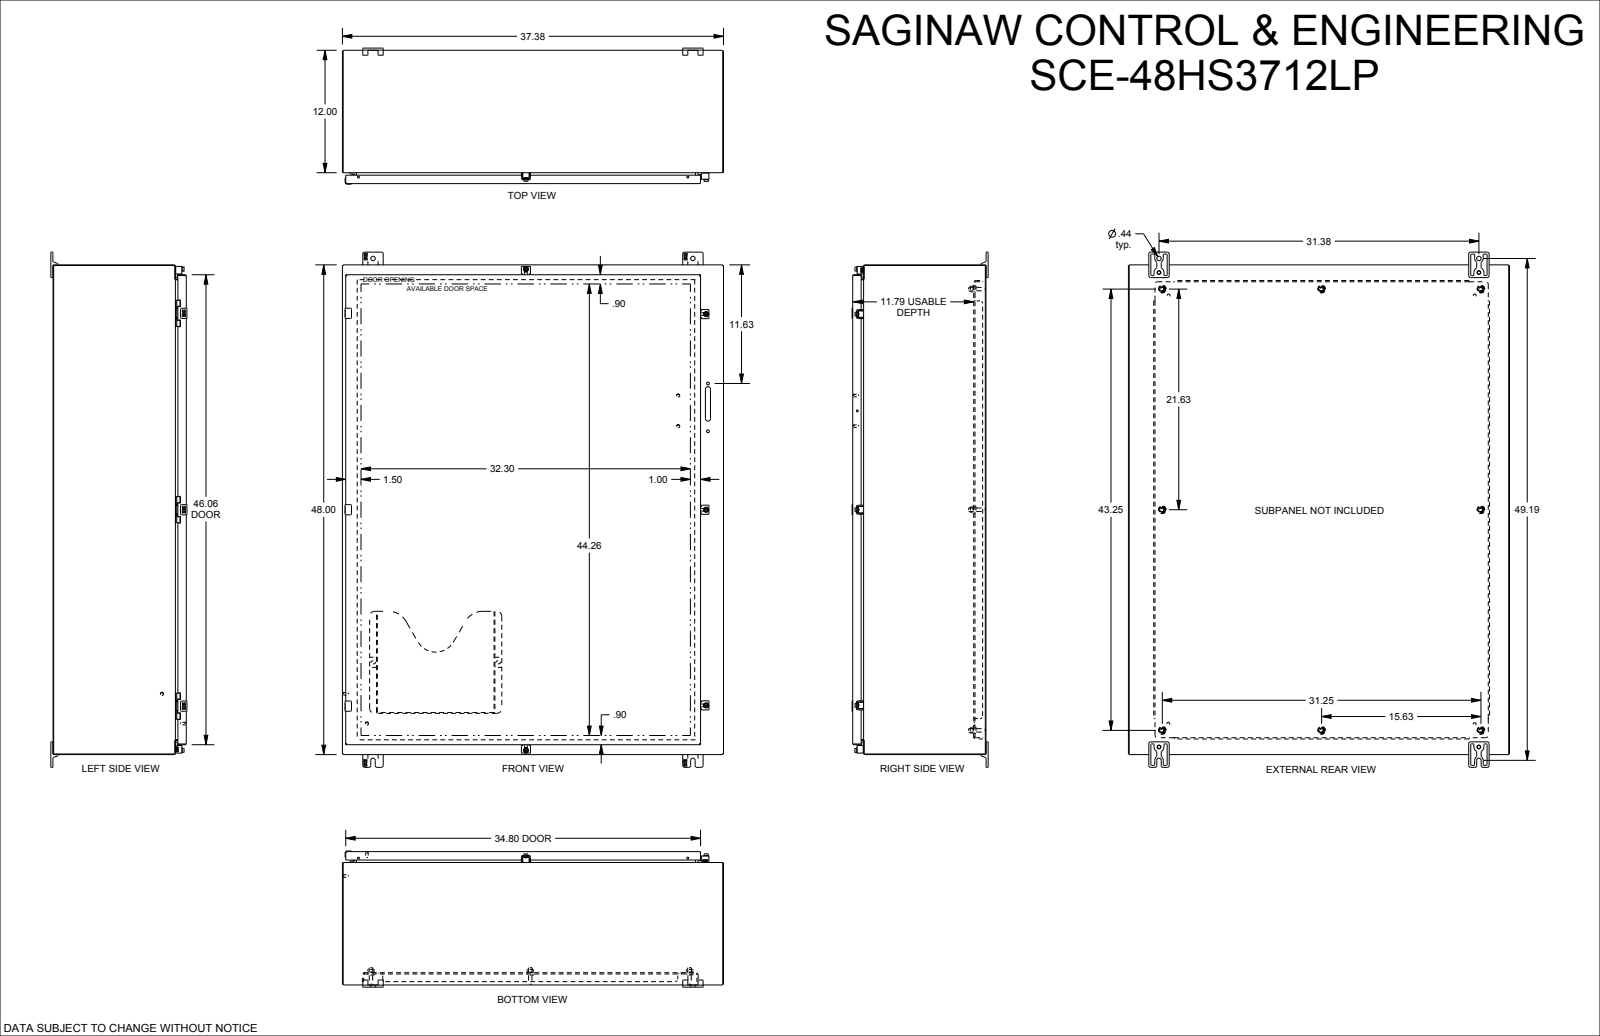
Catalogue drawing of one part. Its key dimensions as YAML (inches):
part_name: "SCE-48HS3712LP"
step_written_by: "SolidWorks 2021 (AUTOMOTIVE_DESIGN)"
units: inches
bodies: {solids: 81, faces: 3710, planar: 1424, cylindrical: 1110, other: 1176}
overall_size: [50.5, 37.375, 13.343]
volume: 692.3
surface_area: 15851
round_holes:
  - {diameter: 0.367, count: 8}
  - {diameter: 0.5, count: 8}
  - {diameter: 0.172, count: 6}
  - {diameter: 0.205, count: 6}
  - {diameter: 0.244, count: 6}
  - {diameter: 0.281, count: 6}
  - {diameter: 0.312, count: 6}
  - {diameter: 0.375, count: 6}
  - {diameter: 0.203, count: 5}
  - {diameter: 0.31, count: 4}
  - {diameter: 0.04, count: 3}
  - {diameter: 0.218, count: 3}
round_bosses_or_shafts:
  - {diameter: 0.25, count: 11}
  - {diameter: 0.248, count: 11}
  - {diameter: 0.17, count: 9}
  - {diameter: 0.366, count: 8}
  - {diameter: 0.332, count: 8}
  - {diameter: 0.24, count: 6}
  - {diameter: 0.507, count: 5}
  - {diameter: 0.59, count: 4}
partial_cylinders:
  - {radius: 0.01, count: 214}
  - {radius: 0.025, count: 76}
  - {radius: 0.015, count: 28}
  - {radius: 0.185, count: 21}
  - {radius: 0.04, count: 20}
  - {radius: 0.06, count: 16}
  - {radius: 0.06, count: 16}
  - {radius: 0.1, count: 16}
face_to_face_distances: [0.075, 12.993, 13.068, 12.918, 1.125, 1.2, 11.868, 11.793, 0.125, 11.918]
hole_center_spacings: [46.5, 23.251, 38.003, 38.79, 43.037, 45.986, 56.095, 0.494]
